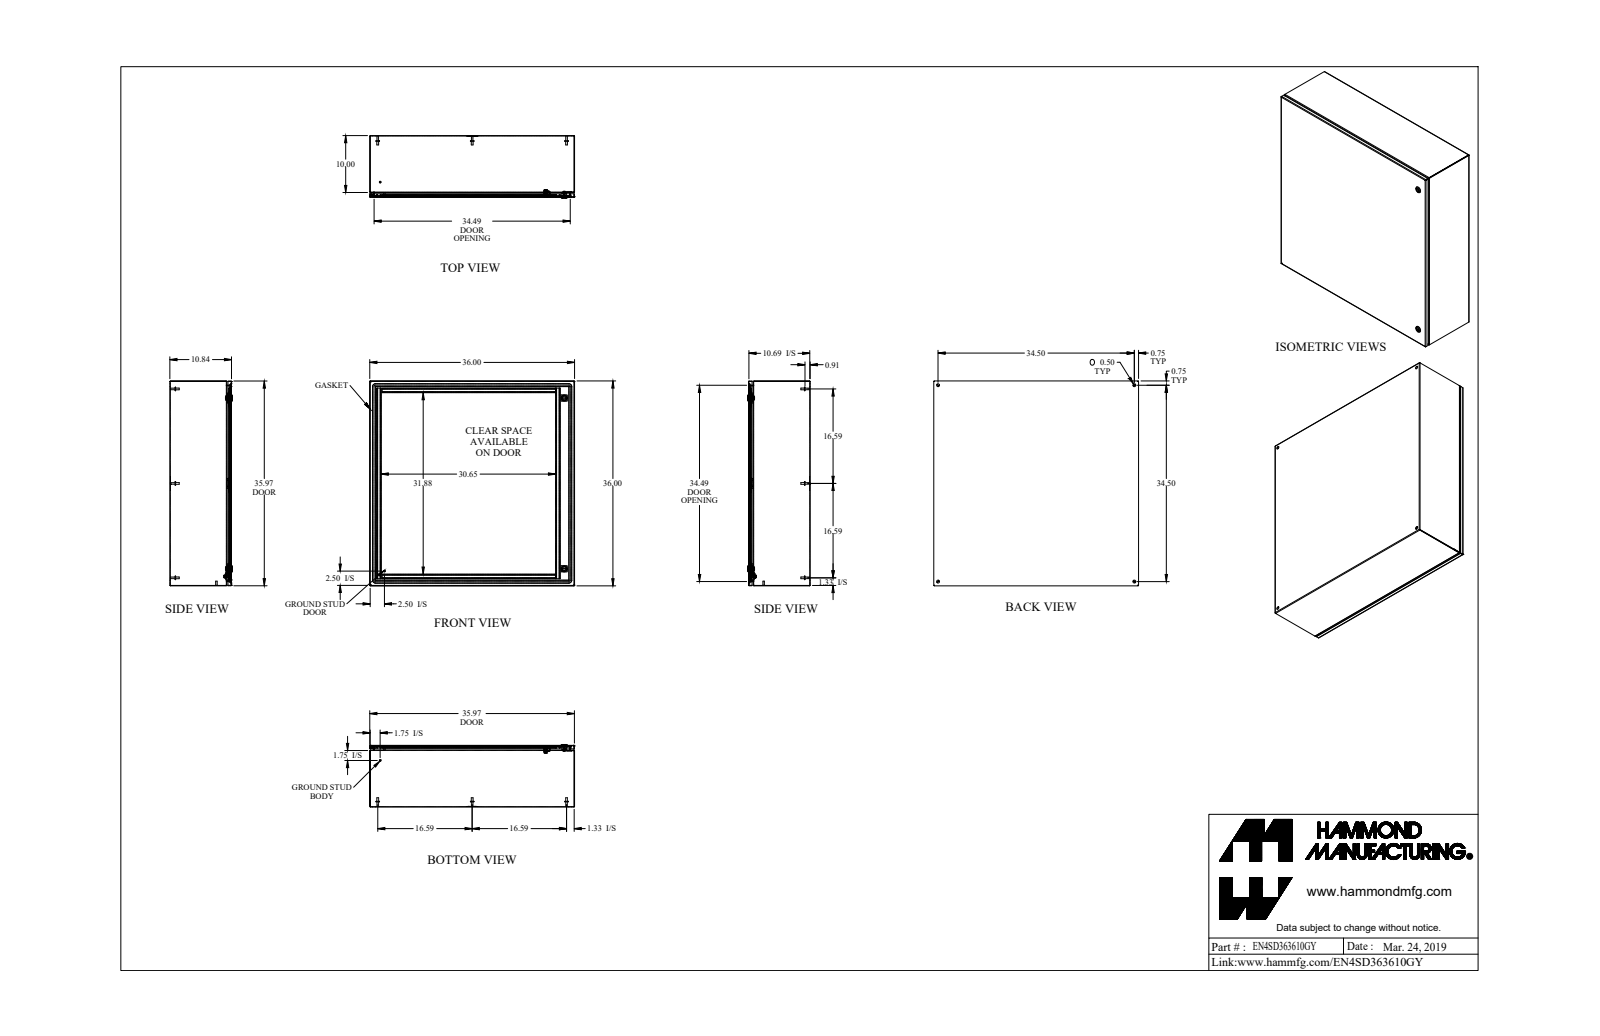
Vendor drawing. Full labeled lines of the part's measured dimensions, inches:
Part name (STEP PRODUCT): EN4SD363610GY
STEP written by: SolidWorks 2019 (AUTOMOTIVE_DESIGN)
Units: inches
Bodies: 41 solids, 1184 faces (555 planar, 394 cylindrical, 235 other)
Overall size (bounding box): 36 × 36 × 10.997
Volume: 334.4 in³ · Surface area: 9 450 in²
Round holes (diameter × count): ⌀0.5 ×4, ⌀0.232 ×2, ⌀0.625 ×2, ⌀0.785 ×2, ⌀0.172 ×1, ⌀0.196 ×1, ⌀0.24 ×1, ⌀0.242 ×1, ⌀0.275 ×1, ⌀0.375 ×1
Round bosses / shafts (diameter × count): ⌀0.313 ×8, ⌀0.27 ×8, ⌀0.625 ×6, ⌀0.625 ×3, ⌀1.1 ×2, ⌀0.525 ×2, ⌀0.281 ×2, ⌀0.25 ×2
Partial cylindrical surfaces — rounded edges, fillets, slot ends (radius × count): R0.043 ×24, R0.081 ×24, R0.036 ×20, R0.108 ×20, R0.062 ×10, R0.094 ×10, R0.312 ×10, R0.016 ×9
Main face-to-face distances: 0.072, 10.765, 35.928, 10.693, 10.837, 35.856, 36, 0.837, 9.928, 0.038
Hole centre spacings: 34.5, 33.502, 48.791, 2.493, 2.494, 3.542, 4.442, 29.999
